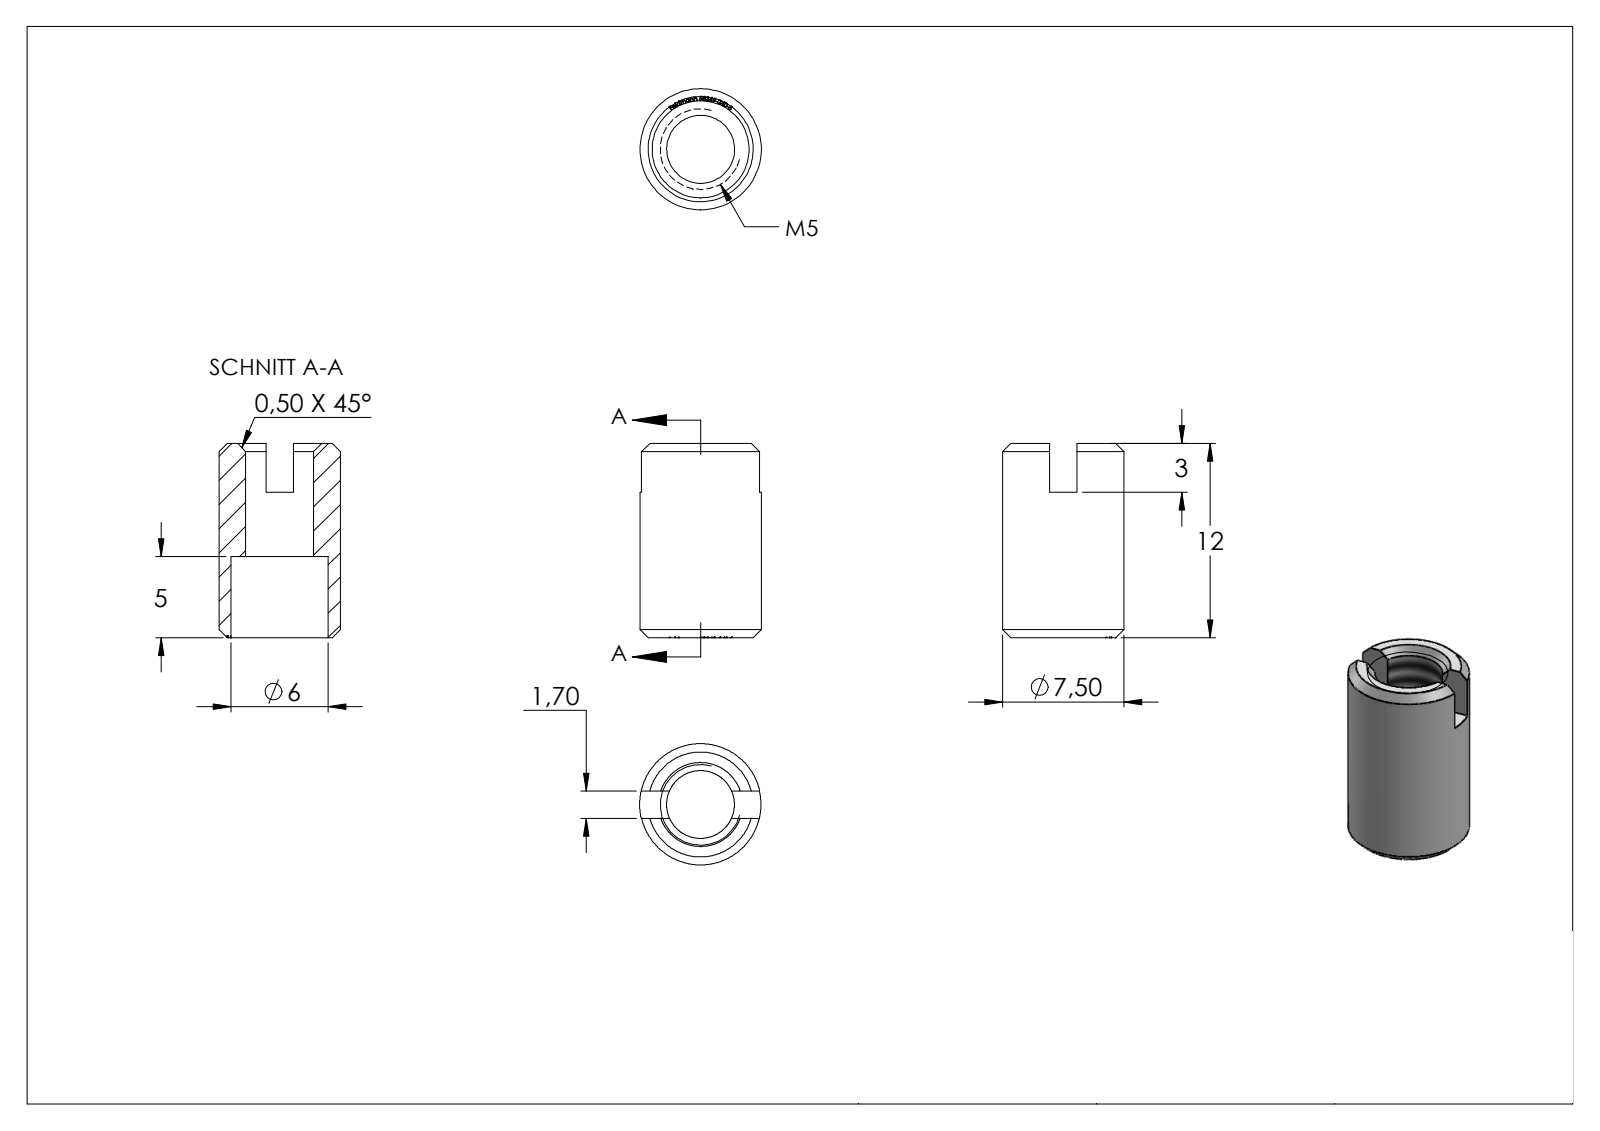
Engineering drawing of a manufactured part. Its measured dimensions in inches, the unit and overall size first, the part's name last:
Units: inches
Overall size (bounding box): 0.472 × 0.295 × 0.295
Round holes (diameter × count): ⌀0.165 ×1, ⌀0.236 ×1
Round bosses / shafts (diameter × count): ⌀0.295 ×1
Main face-to-face distances: 0.067, 0.276, 0.157, 0.118, 0.197, 0.354, 0.472, 0.193, 0.35, 0.469
Volume: 0.016 in³ · Surface area: 0.798 in²
Bodies: 1 solid, 282 faces (140 planar, 3 cylindrical, 139 other)
Part name (STEP PRODUCT): 58369-240-5
STEP written by: SolidWorks 2018 (CONFIG_CONTROL_DESIGN)
